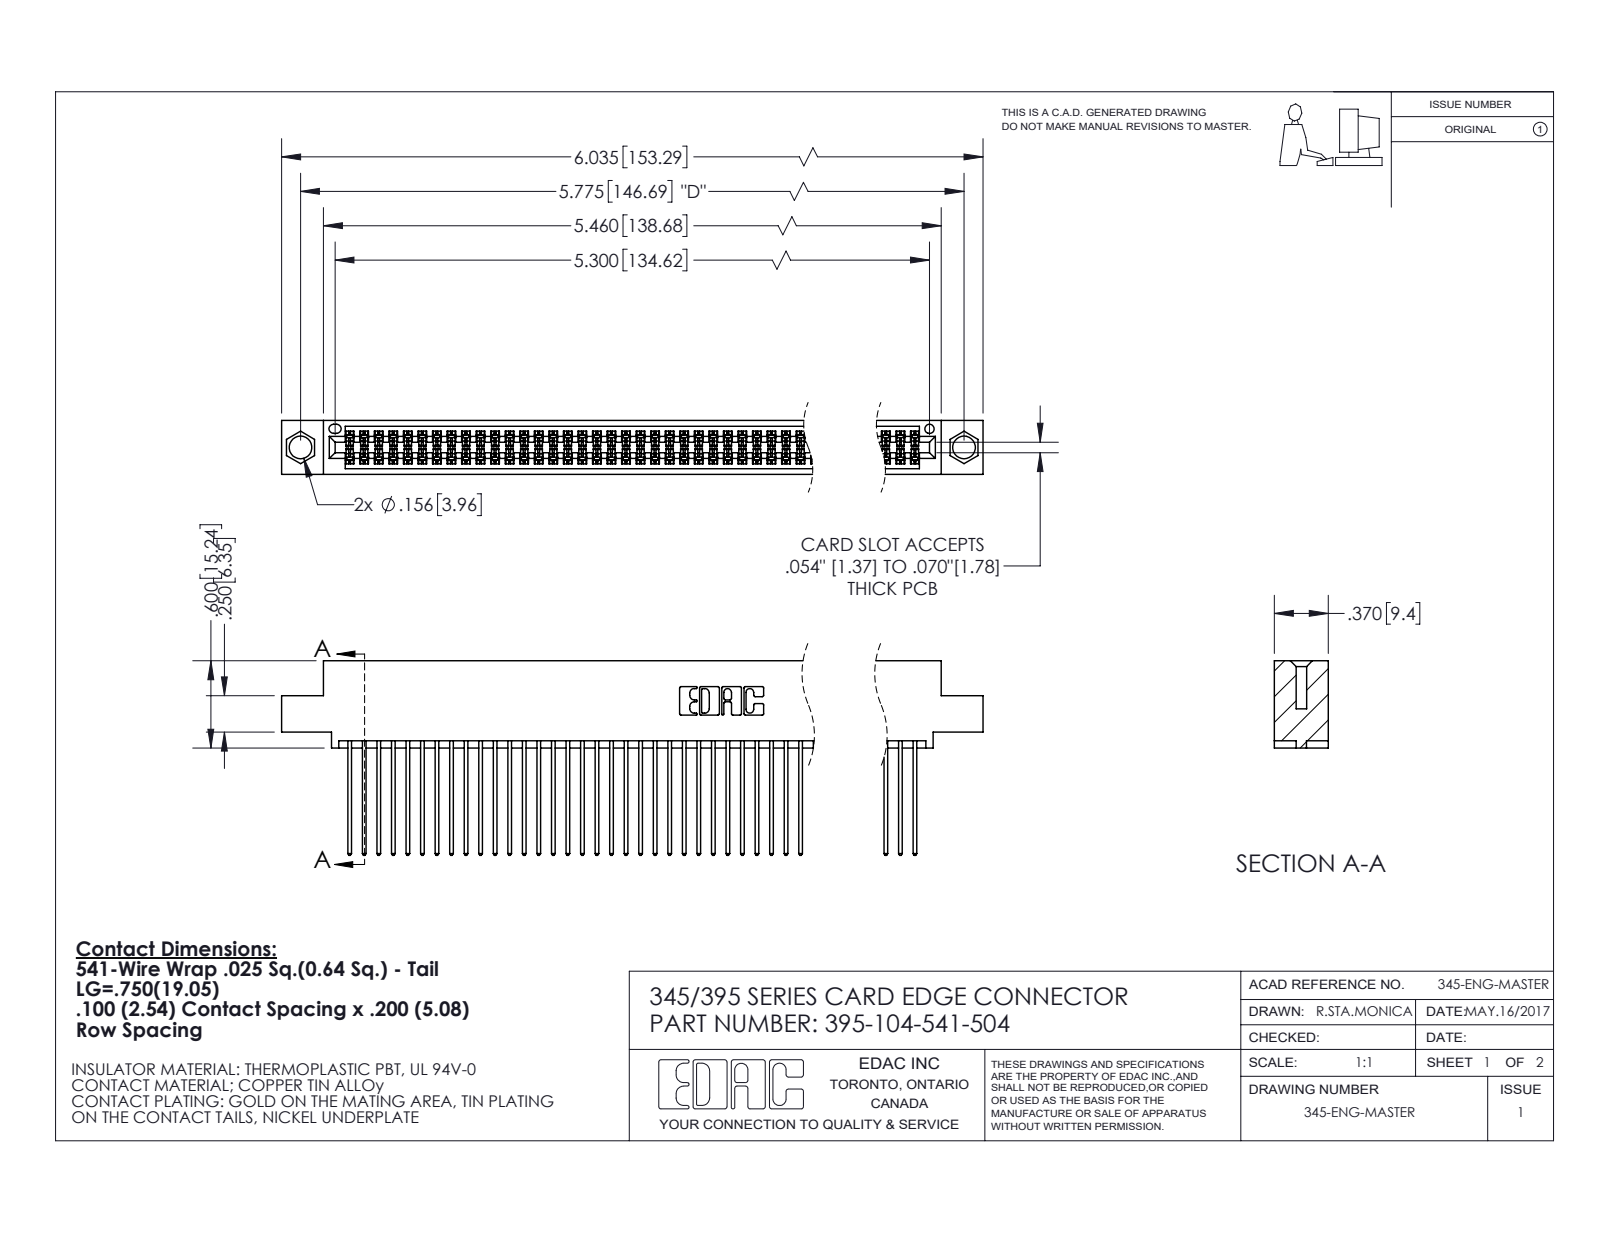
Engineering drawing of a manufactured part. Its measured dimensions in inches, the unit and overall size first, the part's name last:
Units: inches
Overall size (bounding box): 6.035 × 1.337 × 0.37
Round holes (diameter × count): ⌀0.156 ×2, ⌀0.064 ×1
Partial cylindrical surfaces — rounded edges, fillets, slot ends (radius × count): R0.006 ×156, R0.01 ×104, R0.01 ×22, R0.007 ×6, R0.031 ×6, R0.026 ×3, R0.014 ×2, R0.019 ×2
Main face-to-face distances: 0.298, 0.072, 0.2, 0.098, 0.272, 0.025, 0.225, 0.37, 0.175, 0.149
Hole centre spacings: 0.27, 5.539, 5.775
Volume: 0.94 in³ · Surface area: 39.85 in²
Bodies: 105 solids, 5344 faces (3530 planar, 1814 cylindrical, 0 other)
Part name (STEP PRODUCT): 395-104-541-504; 345 Part_0.110 Offset - 0.156 Dia-TI; 345-292-001_345-293-141
STEP written by: SolidWorks 2020 (CONFIG_CONTROL_DESIGN)
